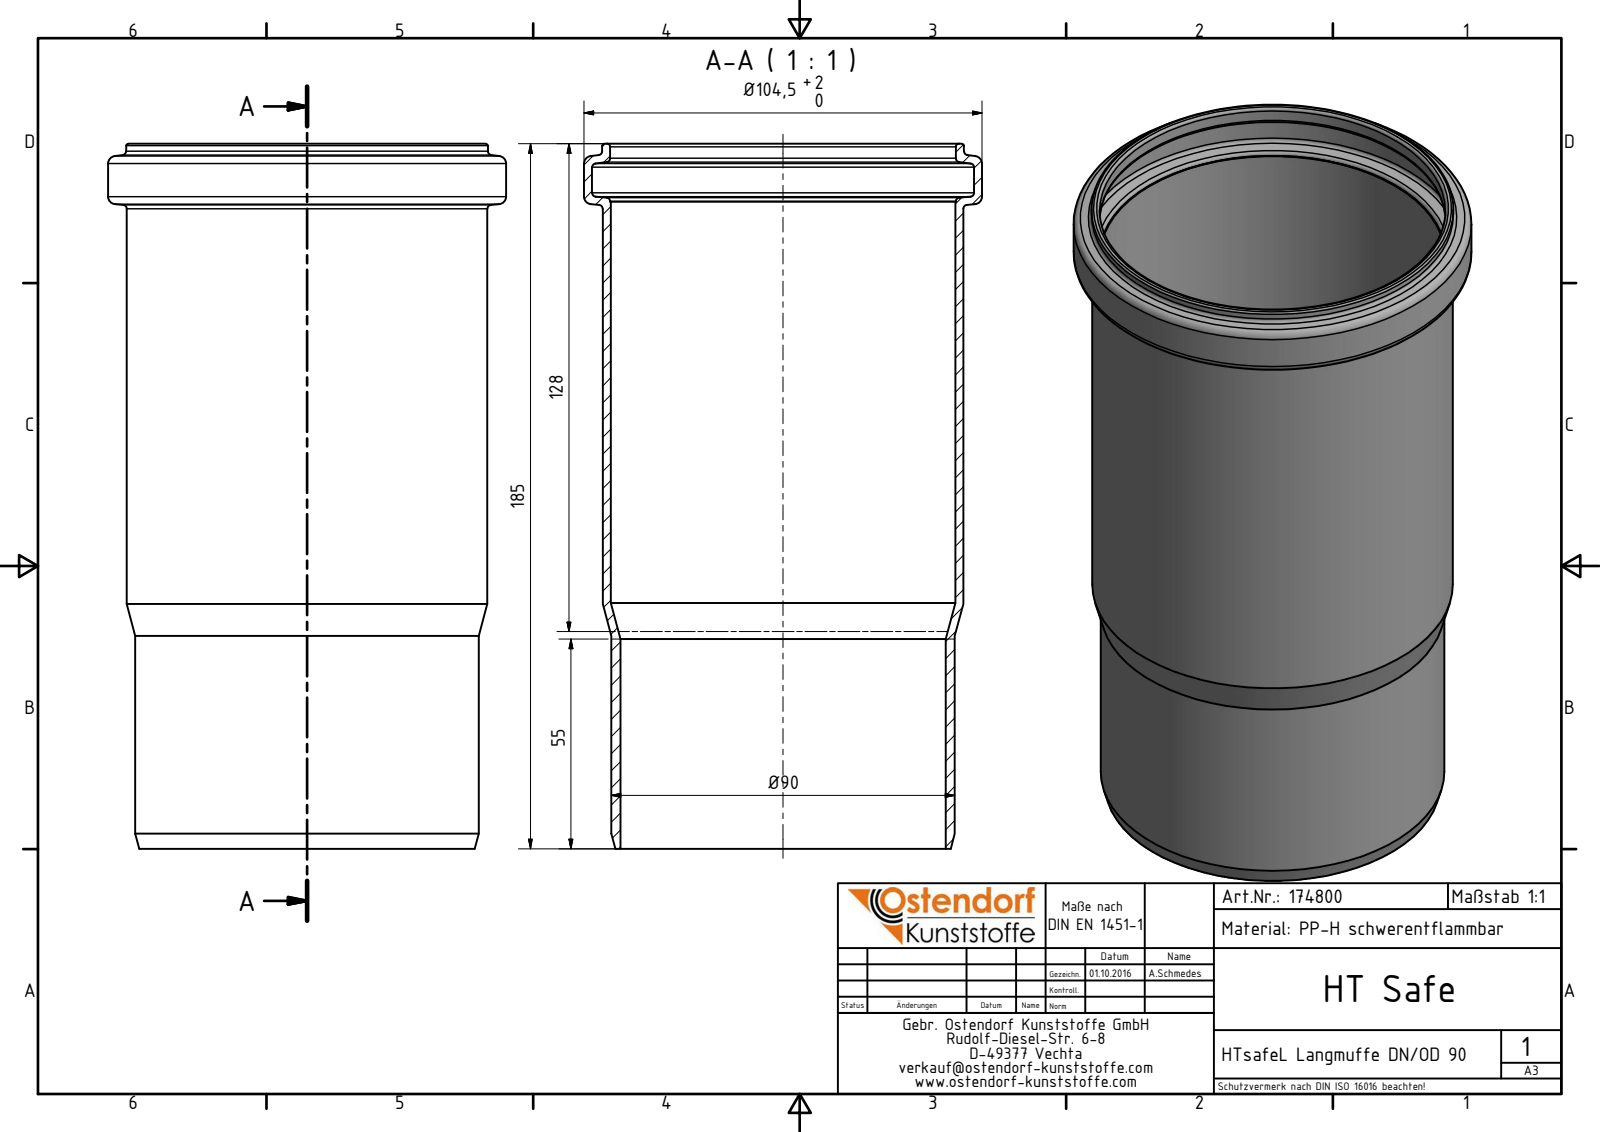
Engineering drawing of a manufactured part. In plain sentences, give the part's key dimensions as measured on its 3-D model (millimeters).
The part is named "174800 HTsafeL DN_OD 90". Its 3-D file was written by "Autodesk Inventor 2016 (AUTOMOTIVE_DESIGN)". It is 1 solid with 29 faces: 3 planar, 9 cylindrical and 17 other. Overall it measures 185 by 104.5 by 104.5 millimeters. Its volume is 121 177 cubic millimeters and its surface area 111 817 square millimeters. Round holes: 1 of diameter 85.4, 1 of diameter 90.5, 1 of diameter 90.8, 1 of diameter 100.3. Round bosses or shafts: 1 of diameter 104.5, 1 of diameter 95, 1 of diameter 94.7, 1 of diameter 90.2. The main face-to-face distances are 185, 169.79, 15.21.
